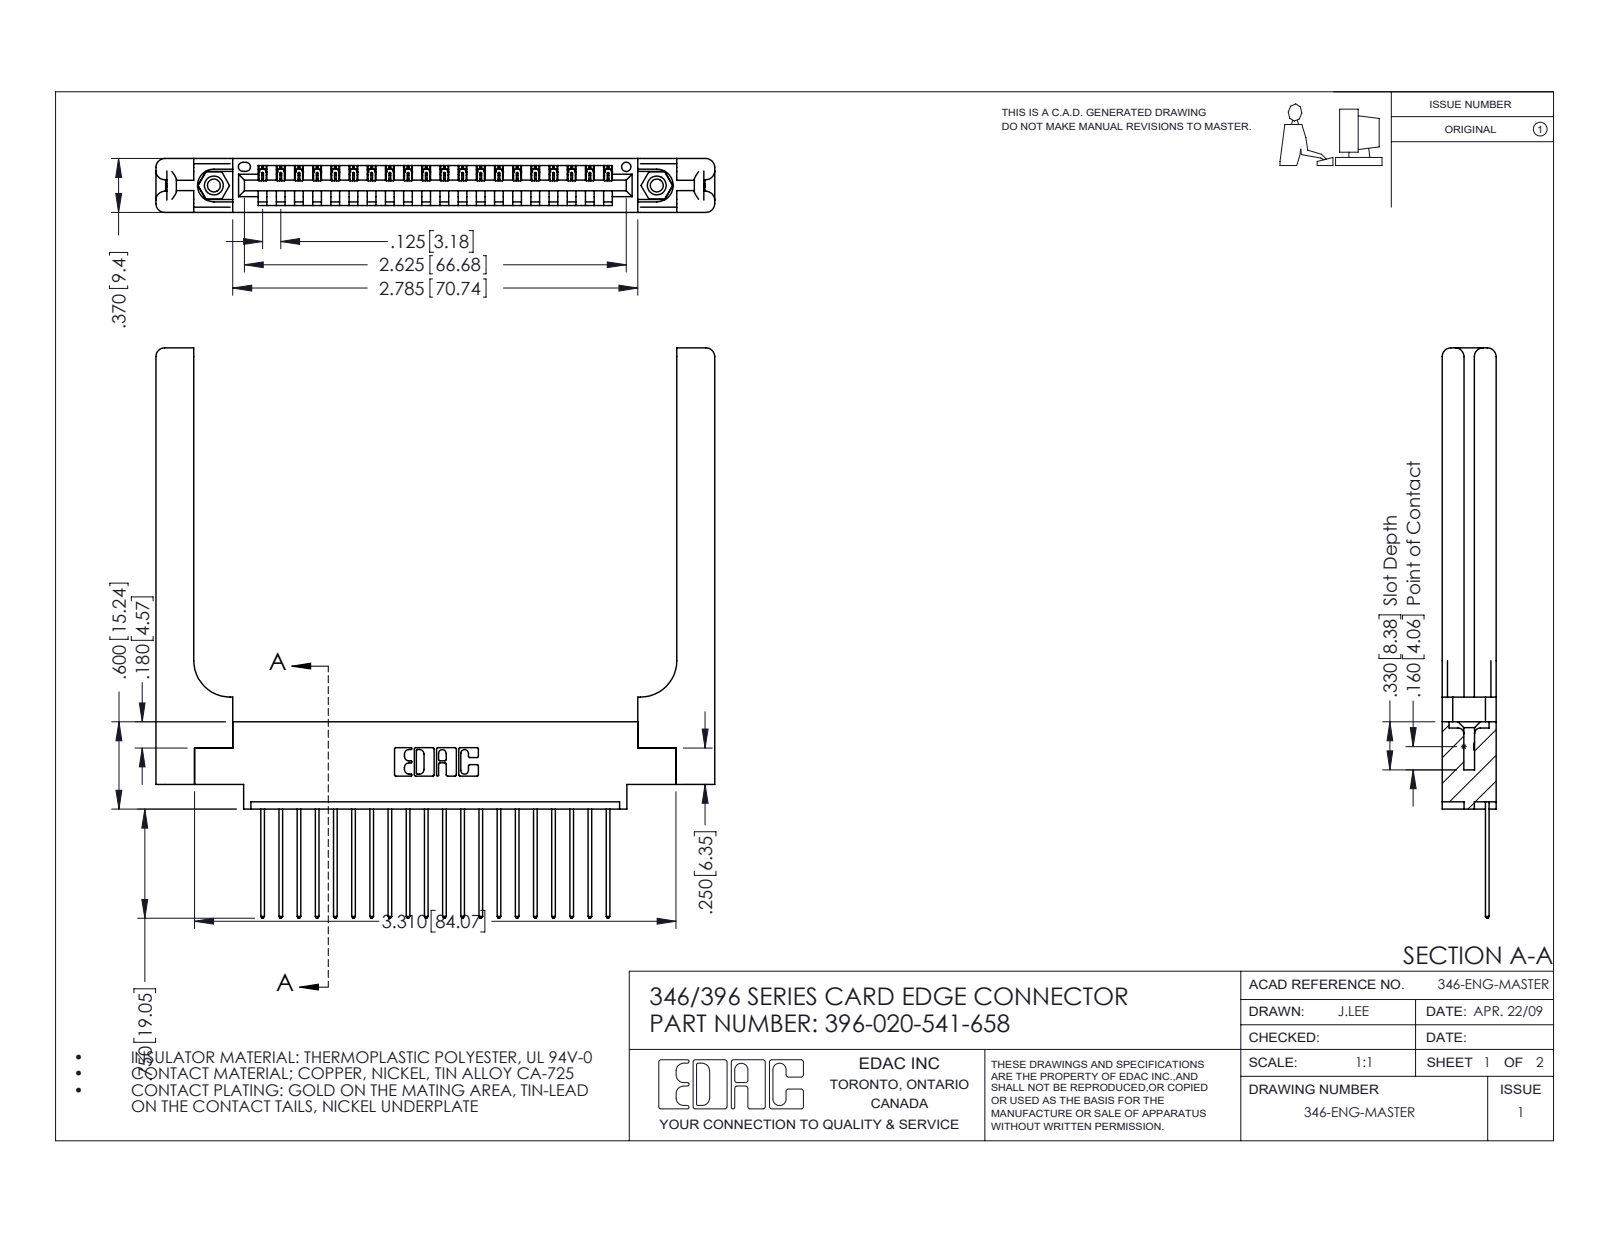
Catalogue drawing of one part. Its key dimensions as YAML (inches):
part_name: "345-250-001_345-250-001-102; 346-220-058_345-220-058; 396-020-541-658; 345-292-001_345-293-141 (+1 more)"
step_written_by: "SolidWorks 2016 (CONFIG_CONTROL_DESIGN)"
units: inches
bodies: {solids: 25, faces: 1542, planar: 1028, cylindrical: 454, other: 60}
overall_size: [3.92, 3.841, 0.37]
volume: 1.014
surface_area: 26.13
round_holes:
  - {diameter: 0.089, count: 2}
  - {diameter: 0.125, count: 2}
  - {diameter: 0.156, count: 2}
  - {diameter: 0.064, count: 1}
round_bosses_or_shafts:
  - {diameter: 0.155, count: 2}
partial_cylinders:
  - {radius: 0.006, count: 40}
  - {radius: 0.01, count: 40}
  - {radius: 0.01, count: 22}
  - {radius: 0.06, count: 16}
  - {radius: 0.007, count: 6}
  - {radius: 0.031, count: 6}
  - {radius: 0.026, count: 3}
  - {radius: 0.03, count: 2}
face_to_face_distances: [0.37, 0.072, 0.048, 0.322, 0.15, 0.148, 0.25, 0.298, 0.025, 0.102]
hole_center_spacings: [0.246, 2.837, 3.045]
